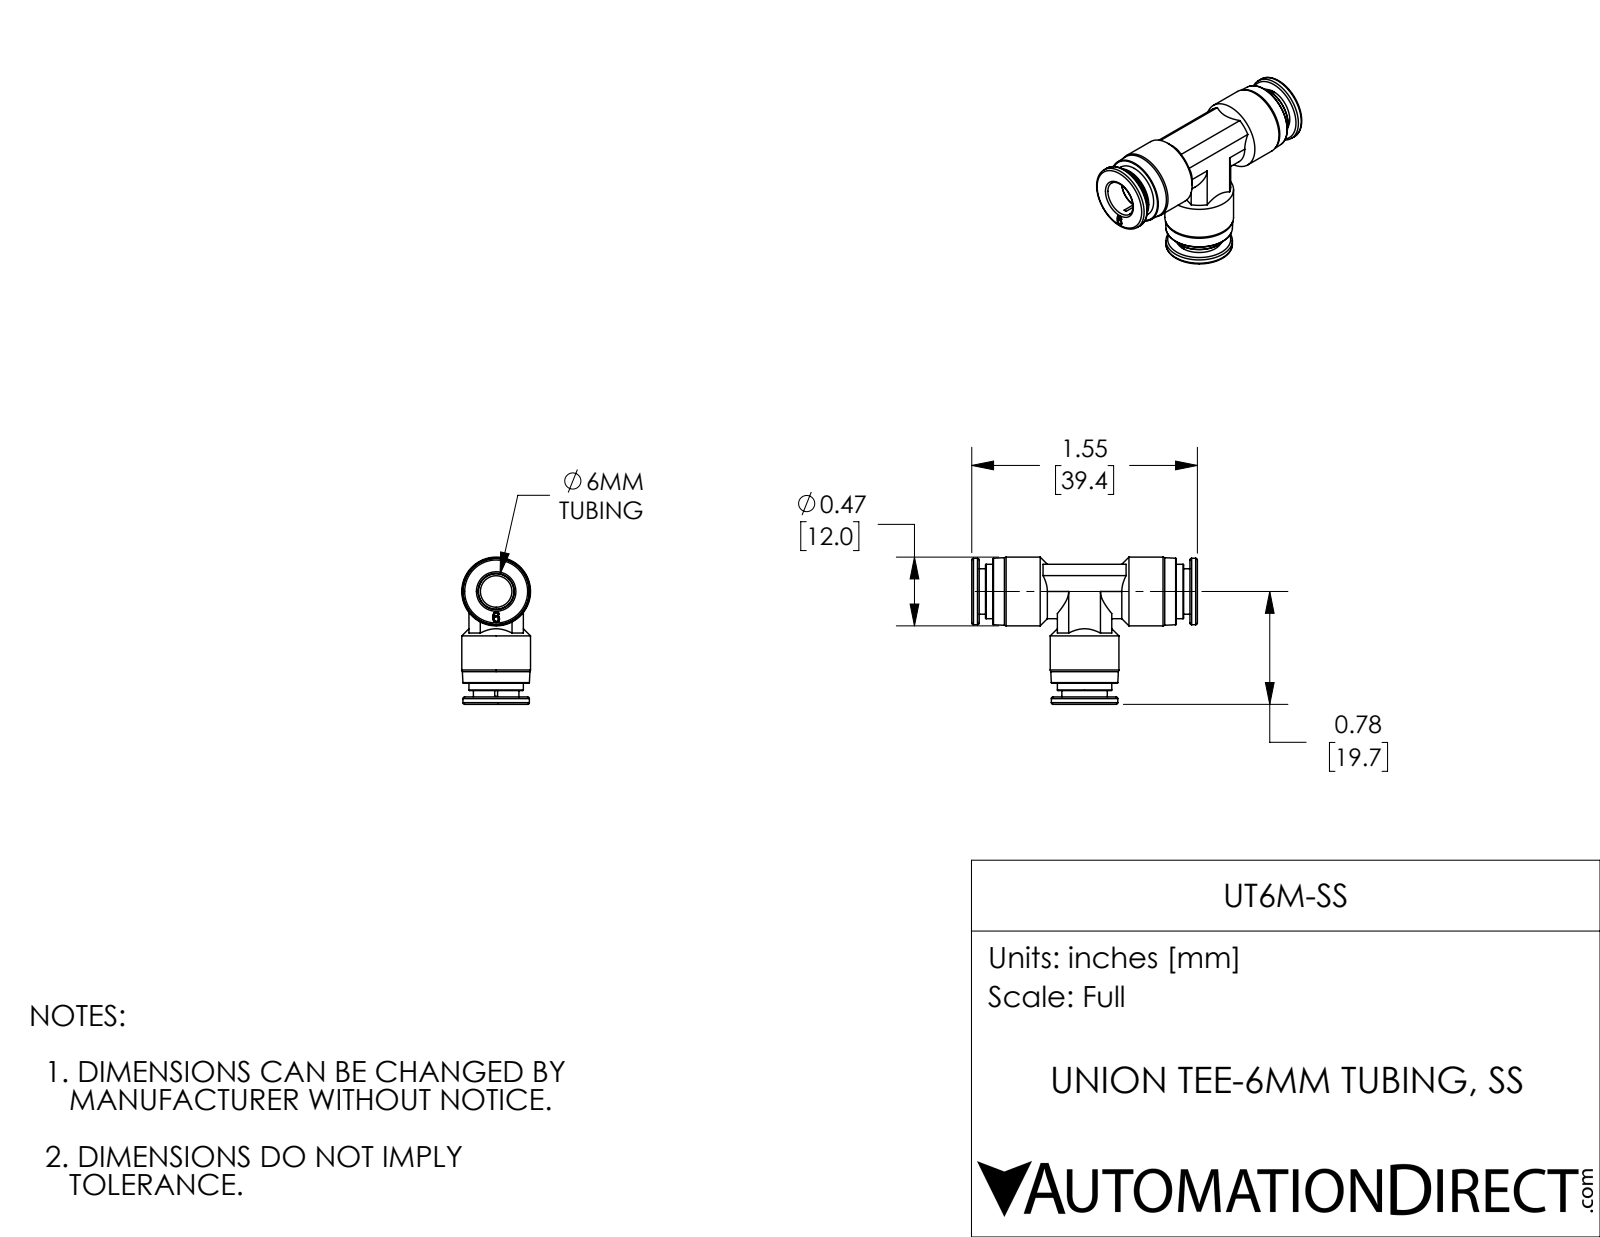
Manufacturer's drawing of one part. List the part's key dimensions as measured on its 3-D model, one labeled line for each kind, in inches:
Part name (STEP PRODUCT): UT6M-SS
STEP written by: SolidWorks 2017 (AUTOMOTIVE_DESIGN)
Units: inches
Bodies: 1 solid, 207 faces (50 planar, 55 cylindrical, 102 other)
Overall size (bounding box): 1.551 × 1.012 × 0.472
Volume: 0.213 in³ · Surface area: 5.694 in²
Round holes (diameter × count): ⌀0.217 ×2, ⌀0.244 ×2, ⌀0.248 ×2, ⌀0.319 ×2
Round bosses / shafts (diameter × count): ⌀0.472 ×2, ⌀0.457 ×2, ⌀0.374 ×2, ⌀0.313 ×2
Partial cylindrical surfaces — rounded edges, fillets, slot ends (radius × count): R0.217 ×2
Main face-to-face distances: 0.051, 0.094, 0.146, 1.5, 0.374, 1.406, 0.963, 0.911, 1.354, 0.817
